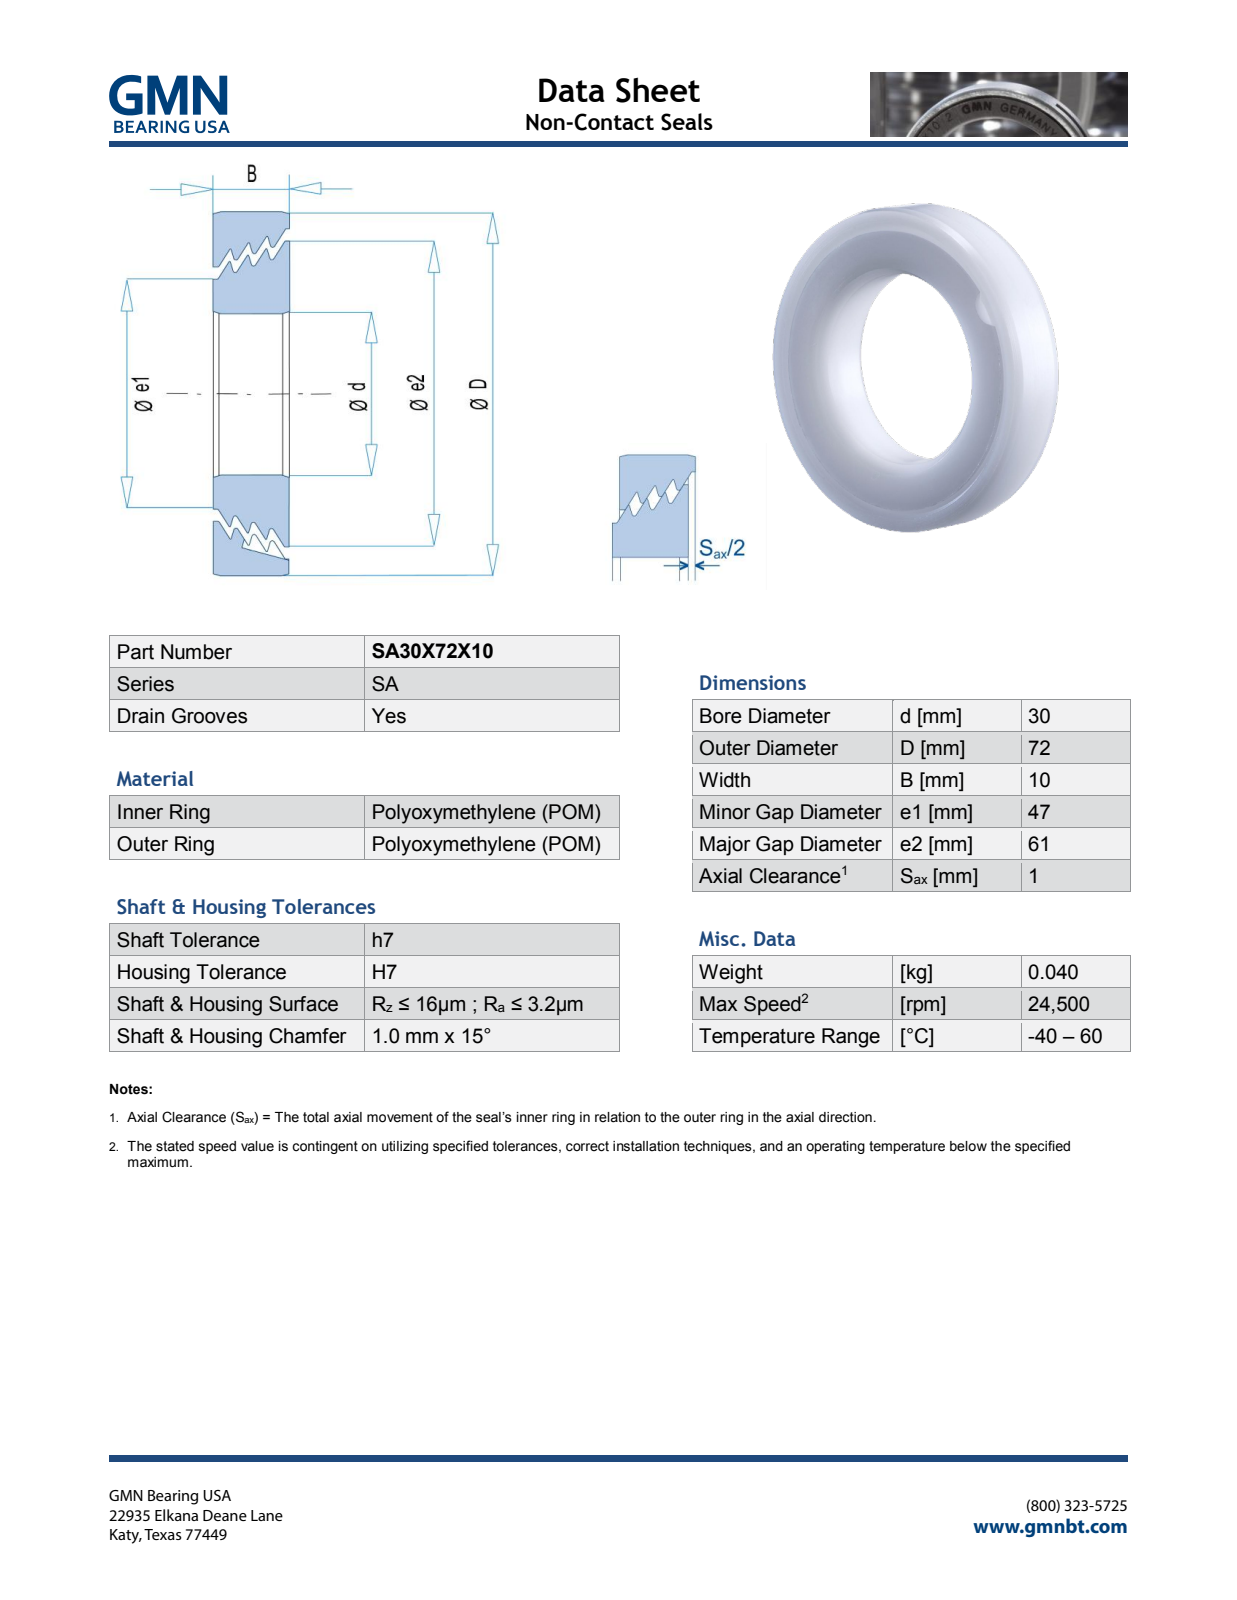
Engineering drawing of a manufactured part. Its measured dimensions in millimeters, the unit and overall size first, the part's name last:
Units: millimetres
Overall size (bounding box): 72 × 72 × 10.07
Round holes (diameter × count): ⌀30 ×1, ⌀48.63 ×1, ⌀62.63 ×1
Round bosses / shafts (diameter × count): ⌀72 ×1, ⌀61 ×1, ⌀47 ×1
Partial cylindrical surfaces — rounded edges, fillets, slot ends (radius × count): R6 ×1
Main face-to-face distances: 10, 10.07, 5.46, 5.39, 4.61, 0.55, 4.38, 3.83, 0.56, 0.54
Volume: 32 113 mm³ · Surface area: 16 382 mm²
Bodies: 2 solids, 641 faces (568 planar, 13 cylindrical, 60 other)
Part name (STEP PRODUCT): SA30X72X10_PRT
STEP written by: PRO/ENGINEER BY PARAMETRIC TECHNOLOGY CORPORATION, 2013150 (AUTOMOTIVE_DESIGN)
